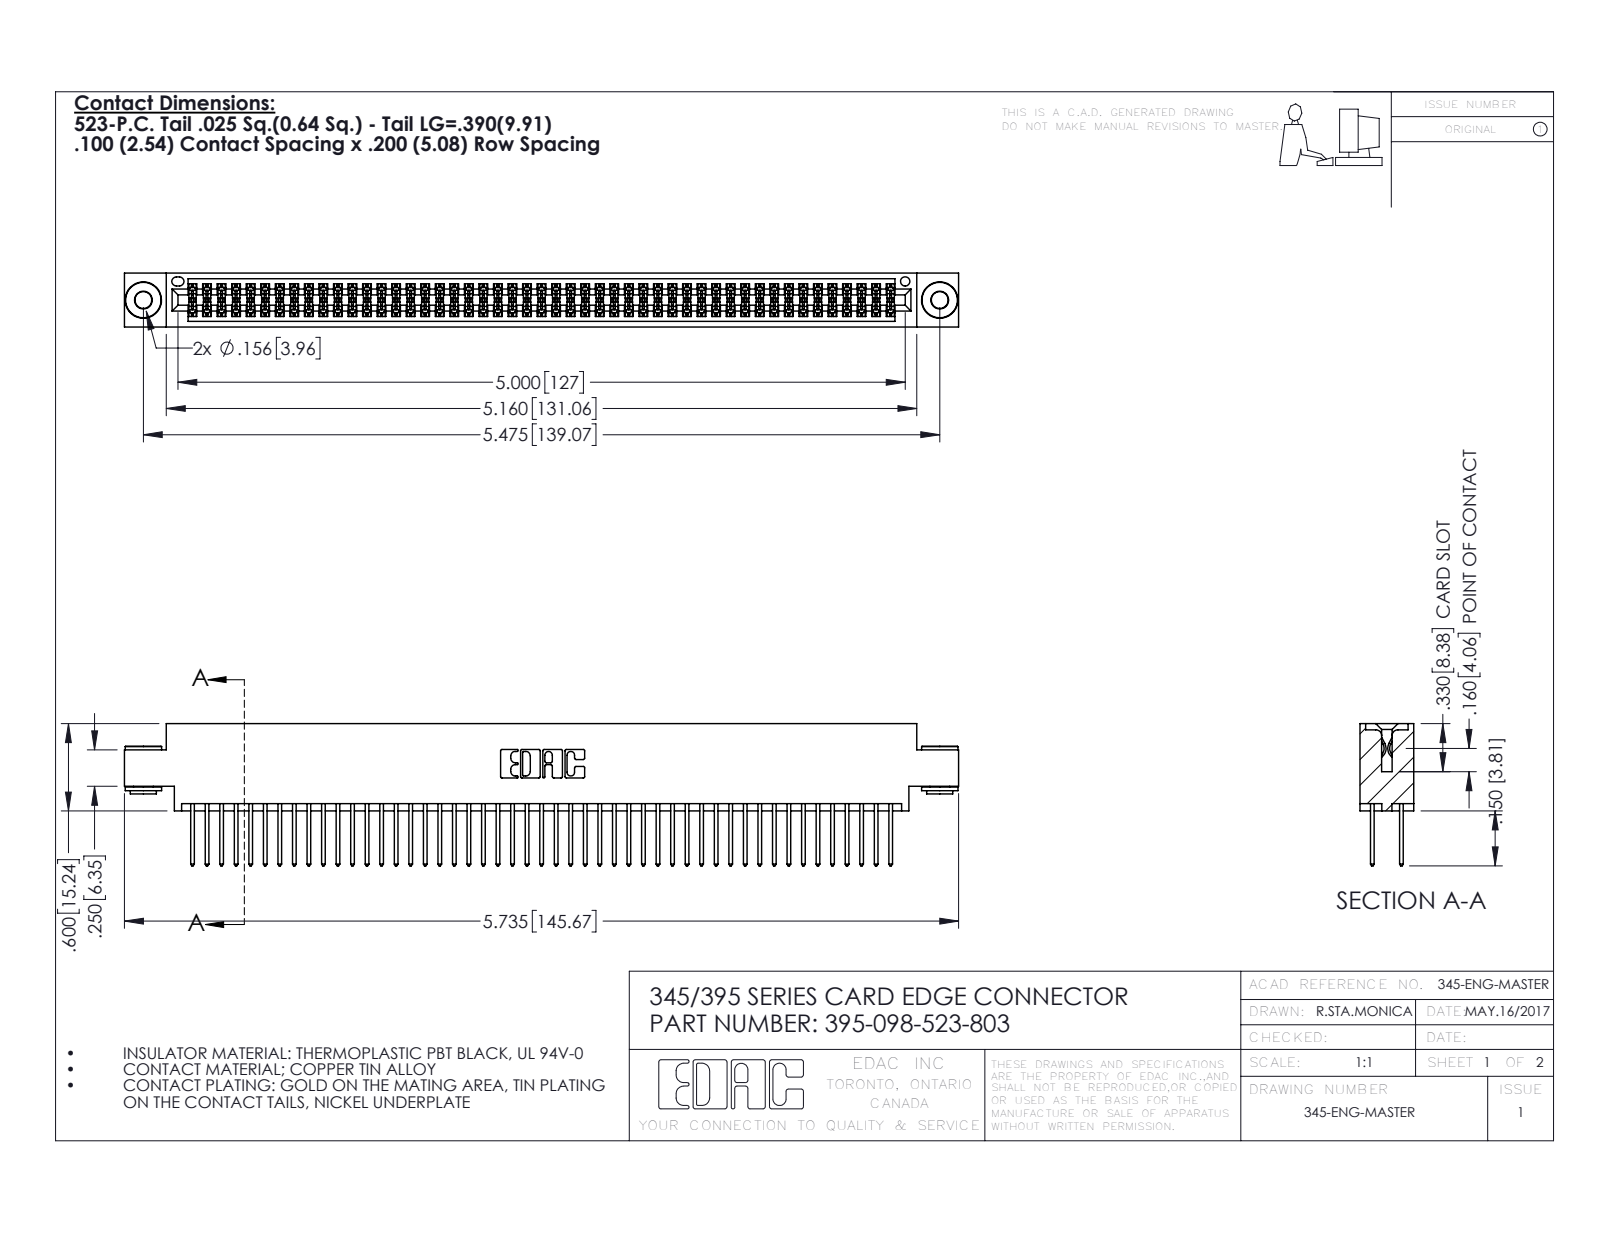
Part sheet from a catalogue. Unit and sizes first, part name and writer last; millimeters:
Units: millimetres
Overall size (bounding box): 145.7 × 24.8 × 9.4
Round holes (diameter × count): ⌀2.9 ×2, ⌀4 ×2, ⌀1.6 ×1
Round bosses / shafts (diameter × count): ⌀6.4 ×2, ⌀4.6 ×2, ⌀3.5 ×2
Partial cylindrical surfaces — rounded edges, fillets, slot ends (radius × count): R0.2 ×147, R0.3 ×98, R0.3 ×22, R0.2 ×6, R0.8 ×6, R0.7 ×3, R0.4 ×2, R0.5 ×2
Main face-to-face distances: 1.8, 7.6, 5.1, 2.5, 6.9, 0.6, 9.4, 5.7, 4.4, 3.8
Hole centre spacings: 6.9, 133.1, 139.1
Volume: 14 300 mm³ · Surface area: 22 550 mm²
Bodies: 101 solids, 5068 faces (3328 planar, 1732 cylindrical, 8 other)
Part name (STEP PRODUCT): 345-250-002_345-250-002-102; 345 Part_0.170 Offset - 0.156 Dia-TH; 395-098-523-803; 345-292-001_345-293-123
STEP written by: SolidWorks 2016 (CONFIG_CONTROL_DESIGN)
